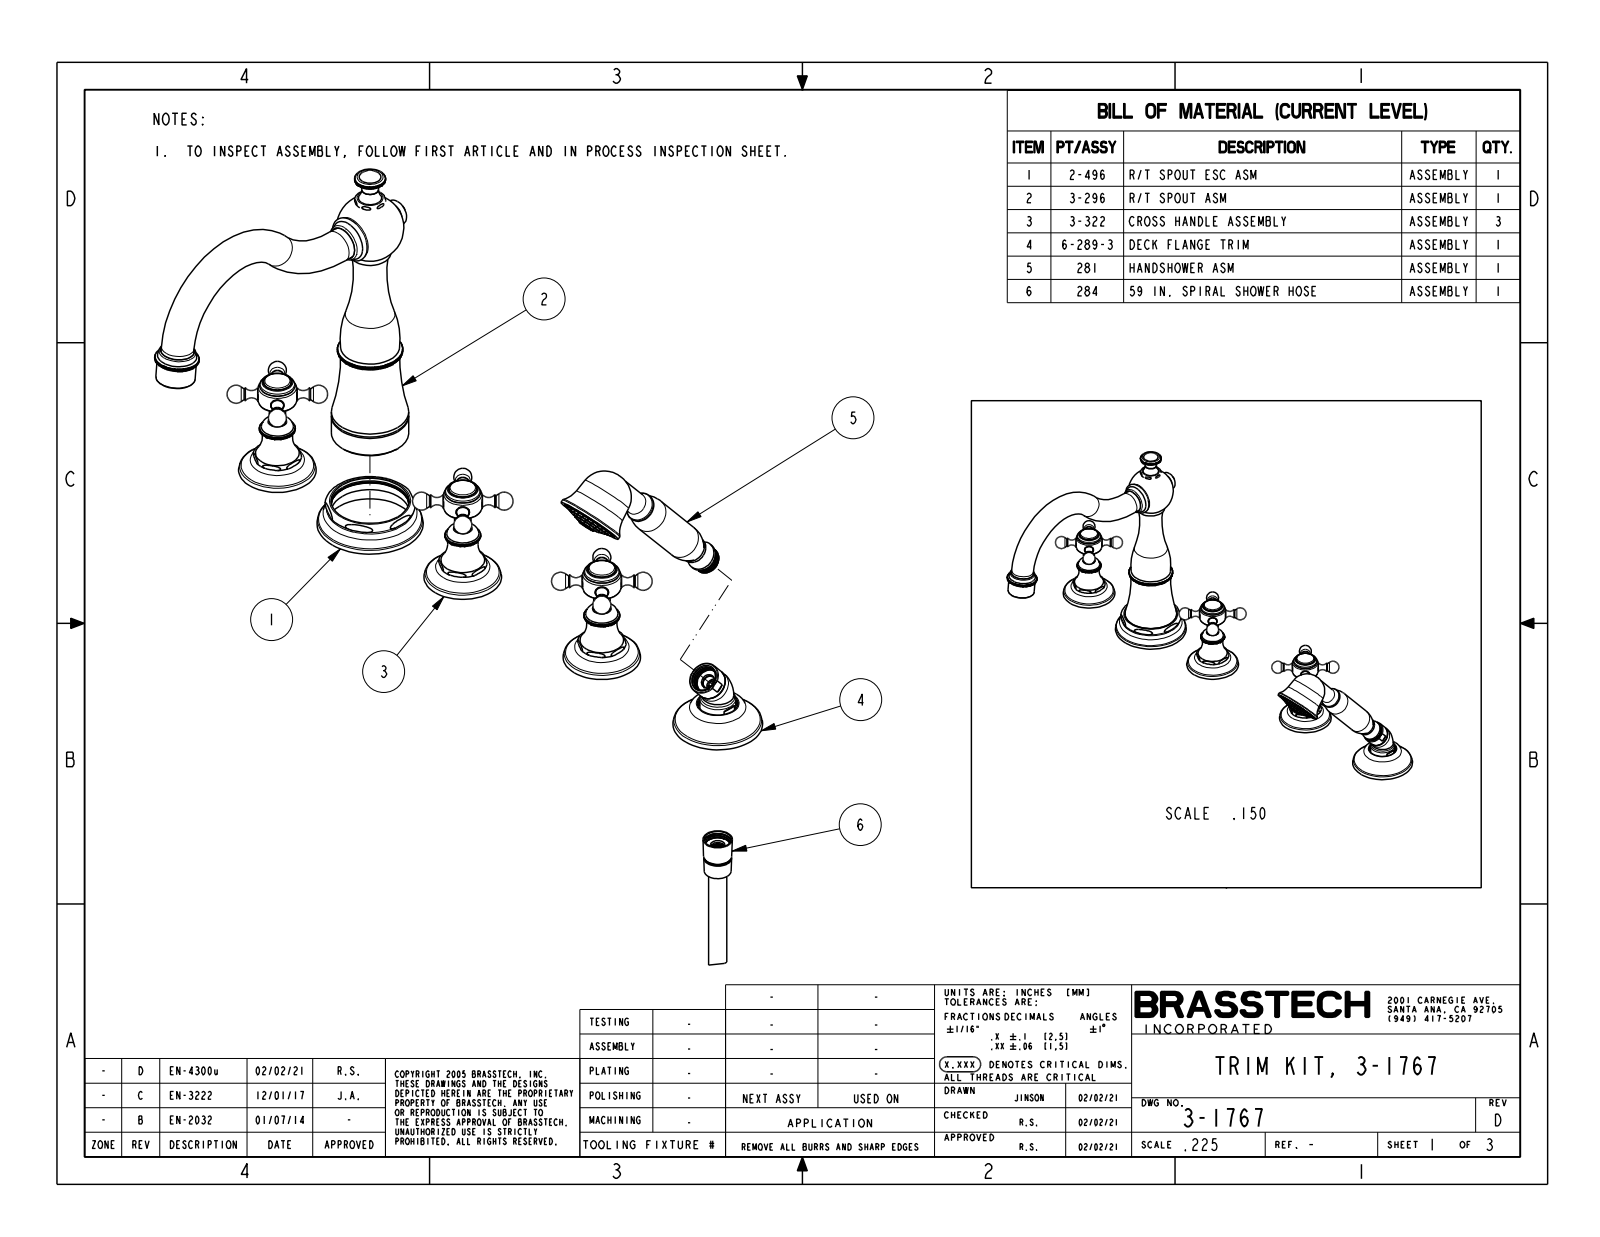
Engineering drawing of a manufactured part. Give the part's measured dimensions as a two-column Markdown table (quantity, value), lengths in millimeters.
| quantity | value |
| --- | --- |
| part name | 3-1767 |
| STEP written by | CREO PARAMETRIC BY PTC INC, 2018400 (CONFIG_CONTROL_DESIGN) |
| units | millimeters |
| bodies | 5 solids, 1774 faces (1100 planar, 213 cylindrical, 461 other) |
| overall size | 547.4 × 270 × 258.3 |
| volume | 911 100 mm³ |
| surface area | 144 600 mm² |
| round holes (diameter × count) | 1.2 × 52, 10.4 × 12, 21.7 × 3 |
| round bosses / shafts (diameter × count) | 10 × 10, 21.3 × 3, 12.7 × 3, 25.4 × 2, 22.9 × 2, 52.8 × 1, 46.3 × 1, 41.9 × 1 |
| partial cylindrical surfaces (radius × count) | 1.3 × 6 |
| main face-to-face distances | 64.5, 34.9, 19.7, 44.8, 21.6, 1.9, 42.9, 66.5, 101.6, 76.2 |
| hole center spacings | 4.7, 9.3, 13.8, 18, 21.9, 107.8, 143.7, 251.5 |
